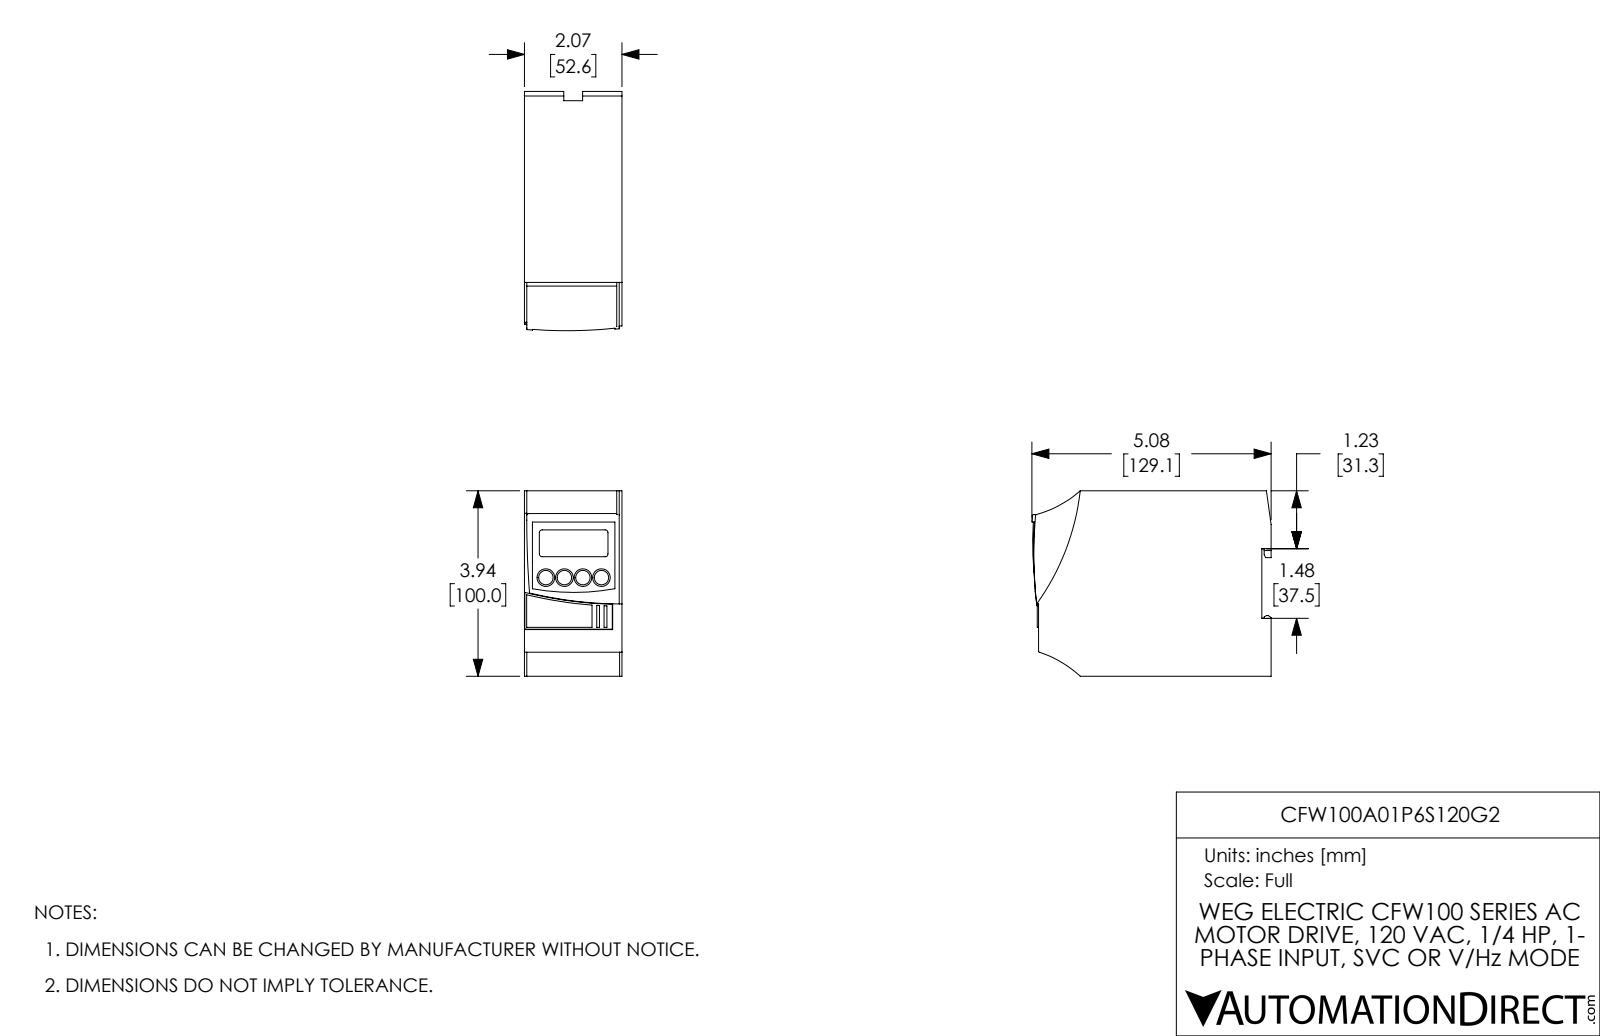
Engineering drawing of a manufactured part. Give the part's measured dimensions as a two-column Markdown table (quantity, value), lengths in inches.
| quantity | value |
| --- | --- |
| part name | CFW100A01P6S120G2 |
| STEP written by | SolidWorks 2017 (AUTOMOTIVE_DESIGN) |
| units | inches |
| bodies | 1 solid, 120 faces (92 planar, 18 cylindrical, 10 other) |
| overall size | 5.082 × 3.937 × 2.073 |
| volume | 37.84 in³ |
| surface area | 77.82 in² |
| partial cylindrical surfaces (radius × count) | 0.059 × 4, 2.362 × 2, 0.012 × 1, 0.02 × 1, 4.912 × 1, 5.118 × 1, 8.52 × 1, 8.528 × 1 |
| main face-to-face distances | 2.072, 3.937, 0.197, 4.941, 4.744, 0.059, 0.51, 3.427, 2.013, 0.836 |
